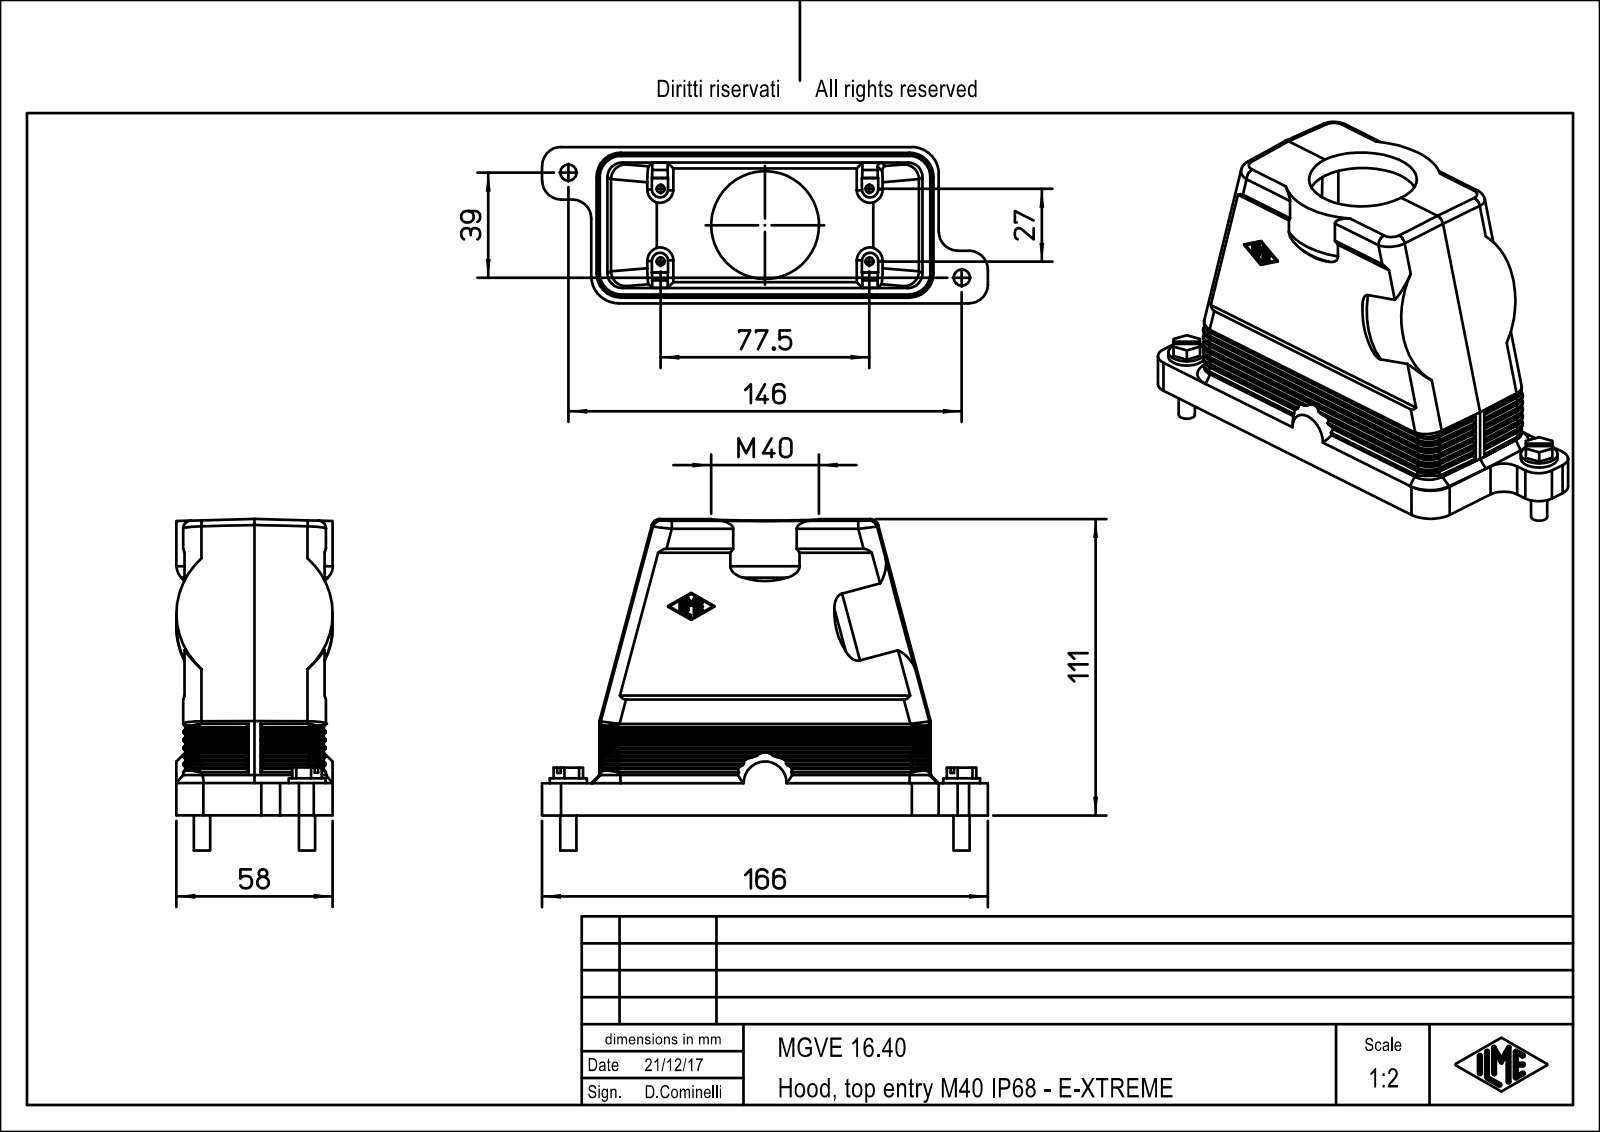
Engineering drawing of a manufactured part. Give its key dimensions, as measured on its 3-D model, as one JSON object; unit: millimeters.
{"part_name": "MGVE_16.40", "step_written_by": "PTC Creo Elements/Direct Modeling 19.0E 27-Jun-2016 (C) Parametric Technology GmbH (AUTOMOTIVE_DESIGN)", "units": "millimeters", "bodies": {"solids": 1, "faces": 534, "planar": 254, "cylindrical": 124, "other": 156}, "overall_size": [165.5, 123, 58], "volume_mm3": 182934, "surface_area_mm2": 84091, "round_holes": [[3, 4], [40, 1]], "round_bosses_or_shafts": [[13.7, 2], [6, 2]], "partial_cylinders_radius": [[7, 62], [0.33, 15], [5.5, 8], [8.5, 4], [0.17, 2], [10, 2], [29, 2], [0.17, 1]], "face_to_face_distances": [52, 3, 55, 2.5, 0.5, 55.5, 52.5, 78, 3.33, 1.67], "hole_center_spacings": [41.03, 27, 77.5, 82.07]}
